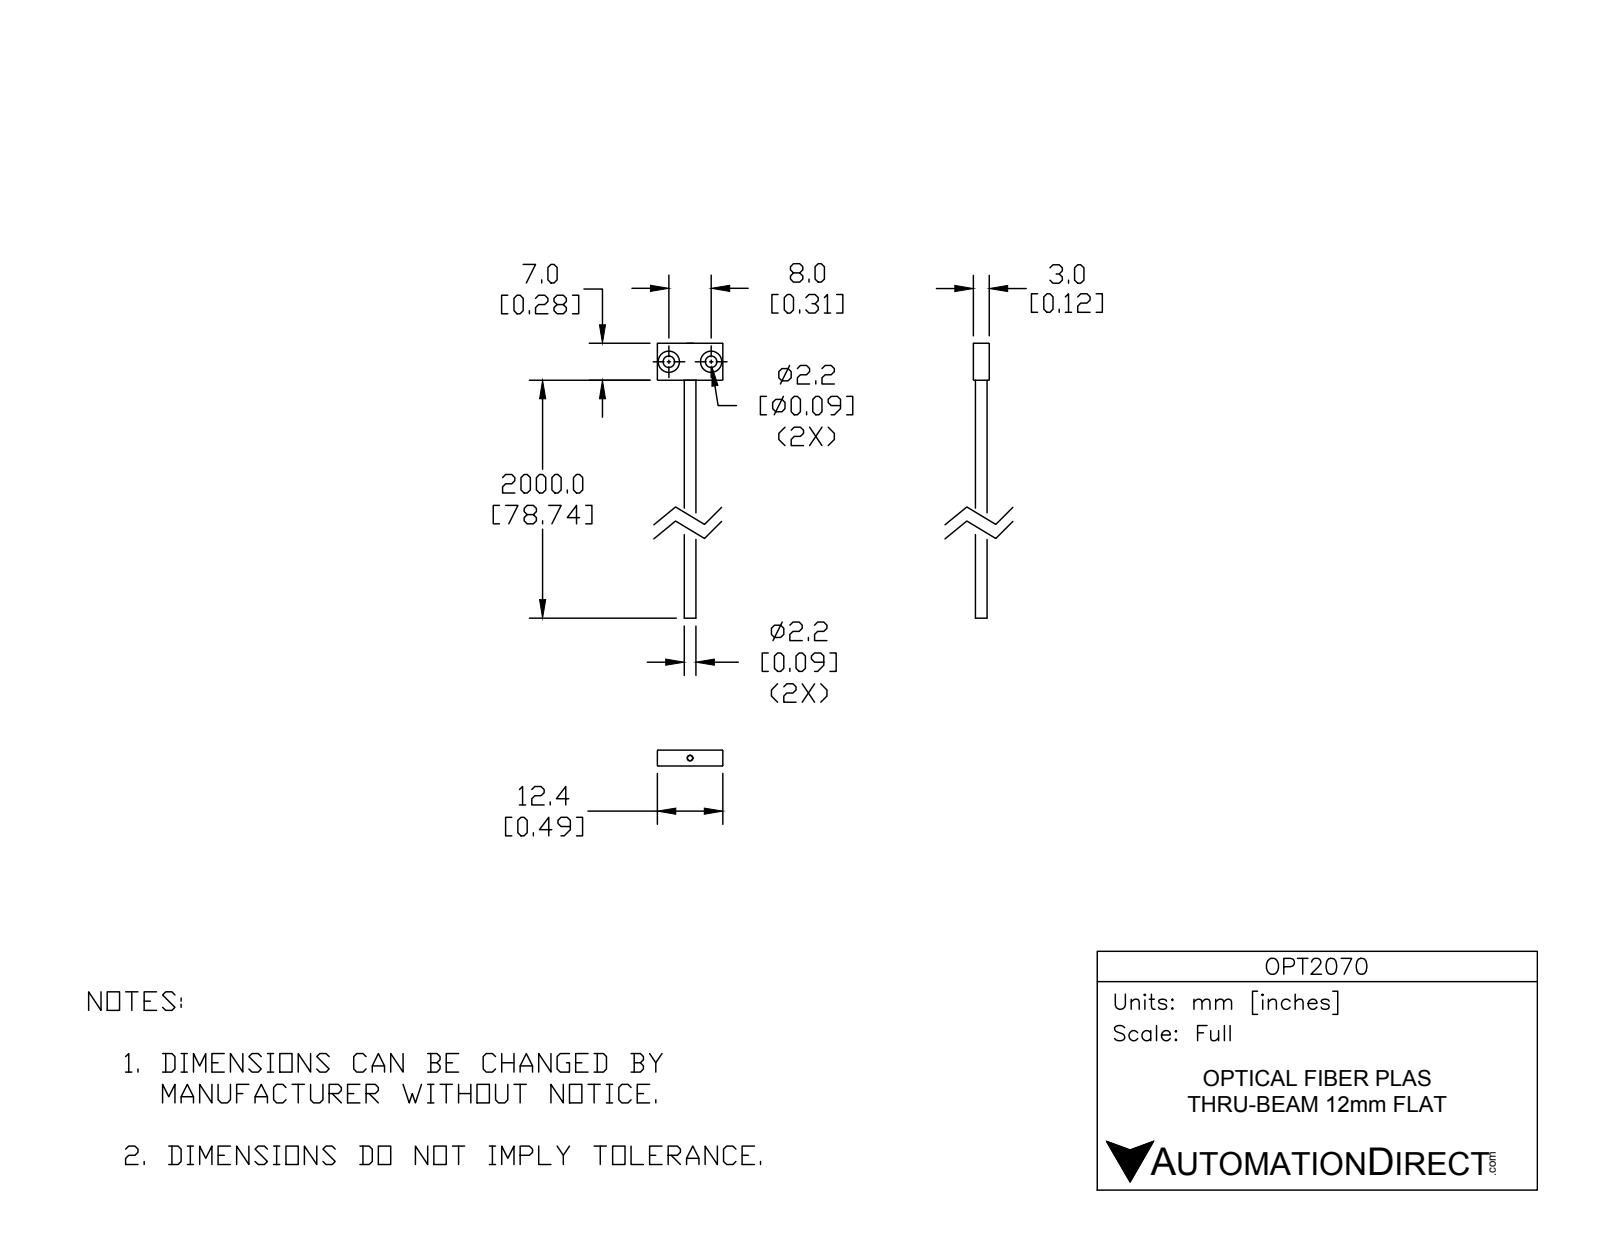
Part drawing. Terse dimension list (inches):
name: OPT2070
written by: SolidWorks 2014 (AUTOMOTIVE_DESIGN)
unit: in
bodies: 1 solid, 50 faces (31 planar, 17 cylindrical, 2 other)
size: 2.185 × 0.488 × 0.118
volume: 0.024 in³; area: 1.06 in²
holes: 2× ⌀0.087, 2× ⌀0.157, 1× ⌀0.043, 1× ⌀0.079
bosses: 1× ⌀0.087, 1× ⌀0.039
face distances: 0.118, 0.276, 0.488, 0.051, 0.067, 1.909, 2.185, 0.272, 0.423, 0.535
hole spacings: 0.176, 0.315
